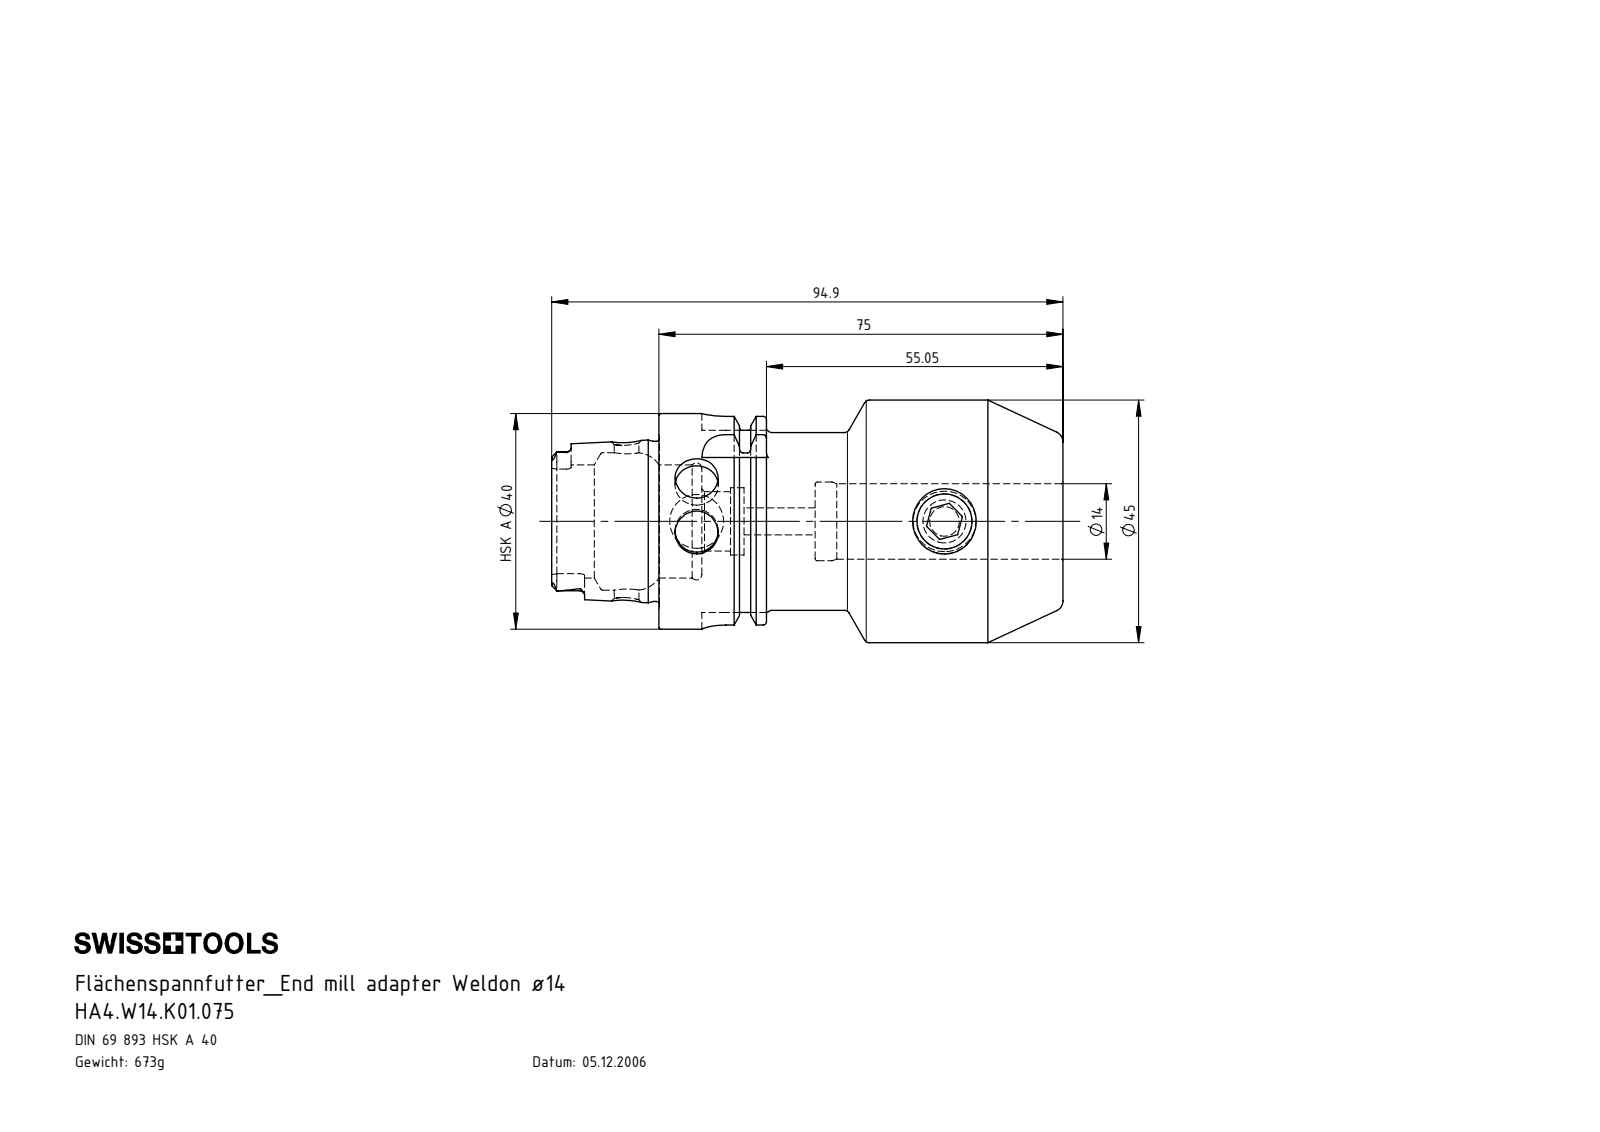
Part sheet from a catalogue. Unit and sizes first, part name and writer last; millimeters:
Units: millimetres
Overall size (bounding box): 94.9 × 45 × 45
Round holes (diameter × count): ⌀8 ×2, ⌀4.6 ×1, ⌀5 ×1, ⌀10 ×1, ⌀10.25 ×1, ⌀11 ×1, ⌀12.5 ×1, ⌀14 ×1, ⌀14.6 ×1, ⌀21 ×1, ⌀25.5 ×1
Round bosses / shafts (diameter × count): ⌀45 ×1, ⌀40 ×1, ⌀34.75 ×1, ⌀33 ×1, ⌀29.71 ×1, ⌀12 ×1
Partial cylindrical surfaces — rounded edges, fillets, slot ends (radius × count): R0.9 ×6, R1.88 ×4, R4.5 ×4
Main face-to-face distances: 75, 7.95, 67.05, 19.95, 12, 55.05, 19.9, 27.85, 39.85, 94.9
Hole centre spacings: 46
Volume: 85 688 mm³ · Surface area: 20 546 mm²
Bodies: 2 solids, 207 faces (58 planar, 60 cylindrical, 89 other)
Part name (STEP PRODUCT): HA4.W14.K01.075; HA4-W14.K01.075_B_Fertigbearbeitung; W12-ER1.001.016
STEP written by: SolidWorks 2017 (CONFIG_CONTROL_DESIGN)
